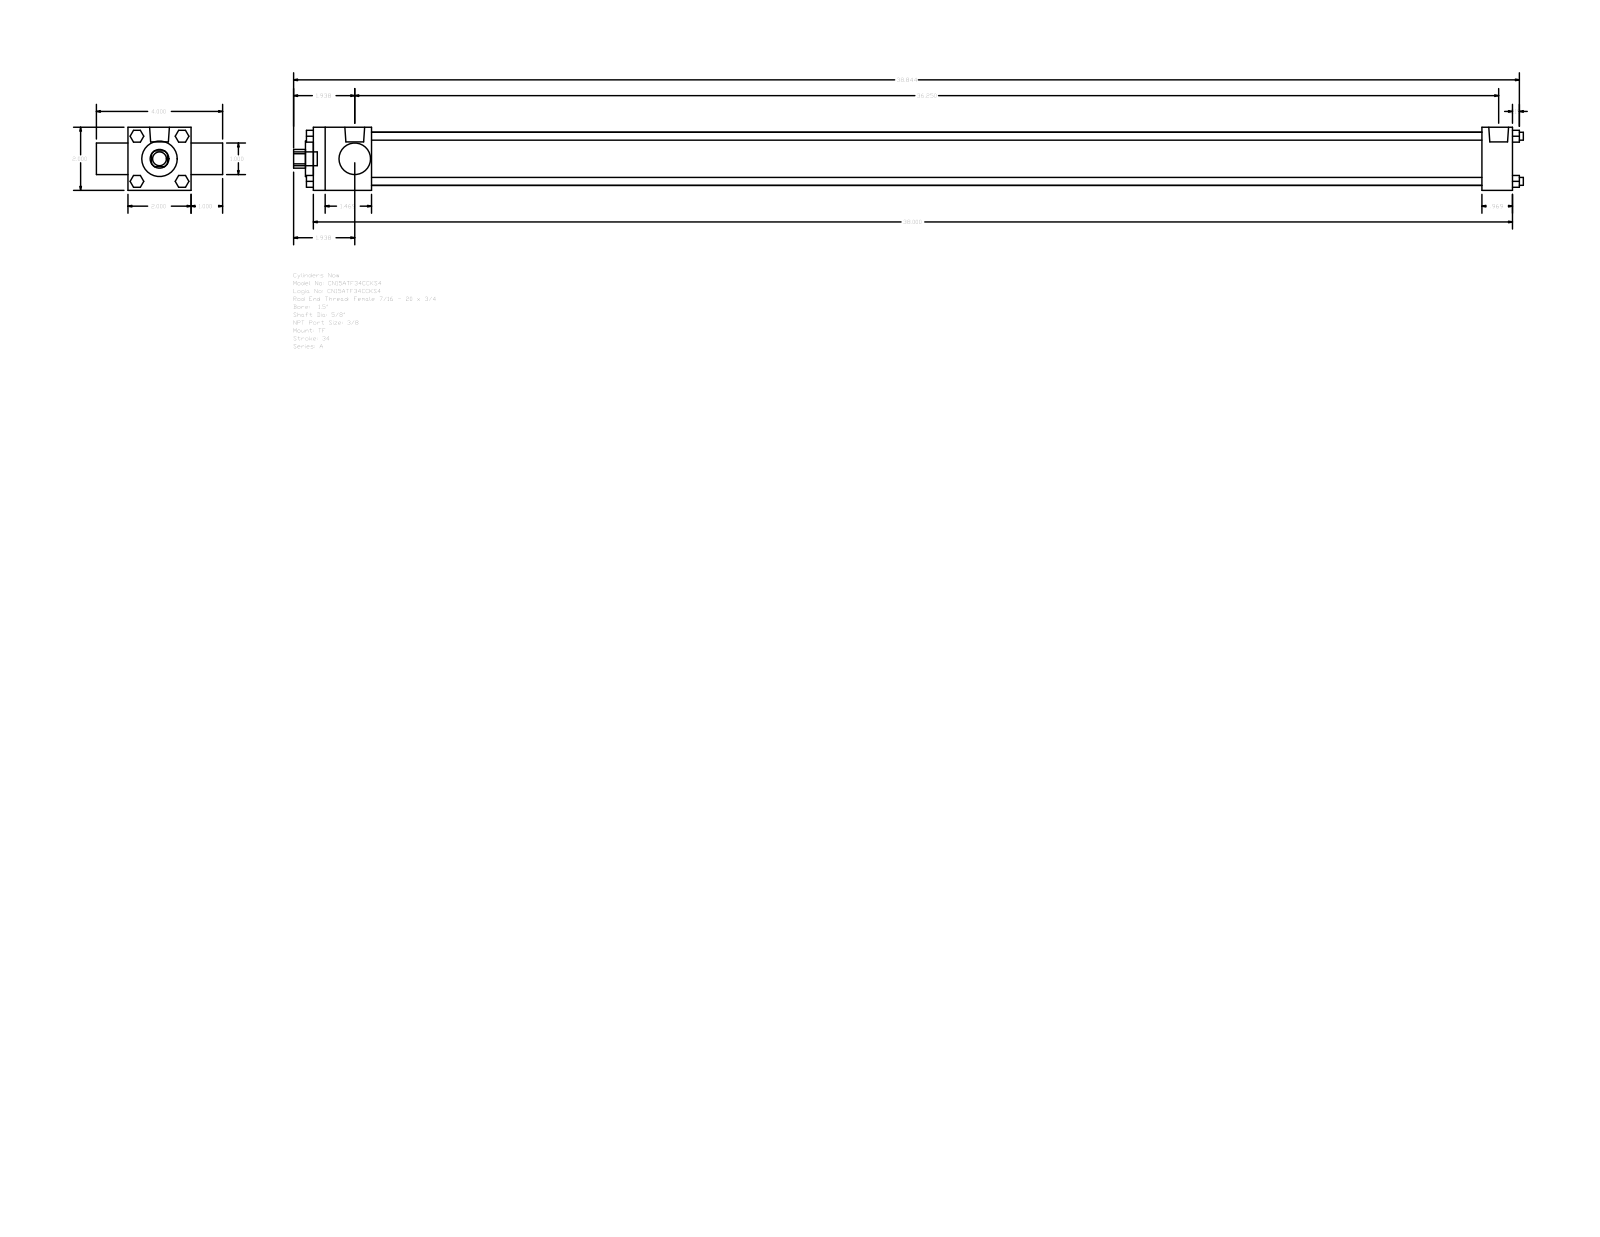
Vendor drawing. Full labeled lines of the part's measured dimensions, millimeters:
Part name (STEP PRODUCT): A_TF__0150_0.625
STEP written by: GSSL Pune (CONFIG_CONTROL_DESIGN)
Units: millimetres
Bodies: 0 solids, 120 faces (92 planar, 28 cylindrical, 0 other)
Overall size (bounding box): 989.81 × 101.6 × 50.8
Round holes (diameter × count): ⌀15.88 ×1, ⌀25.4 ×1, ⌀28.57 ×1, ⌀42.93 ×1
Round bosses / shafts (diameter × count): ⌀6.35 ×4, ⌀5.56 ×3, ⌀15.93 ×2, ⌀11.11 ×1
Partial cylindrical surfaces — rounded edges, fillets, slot ends (radius × count): R7.54 ×1
Main face-to-face distances: 50.8, 965.2, 25.4, 76.2, 46.83, 940.59, 893.76, 918.37, 24.61, 9.52
